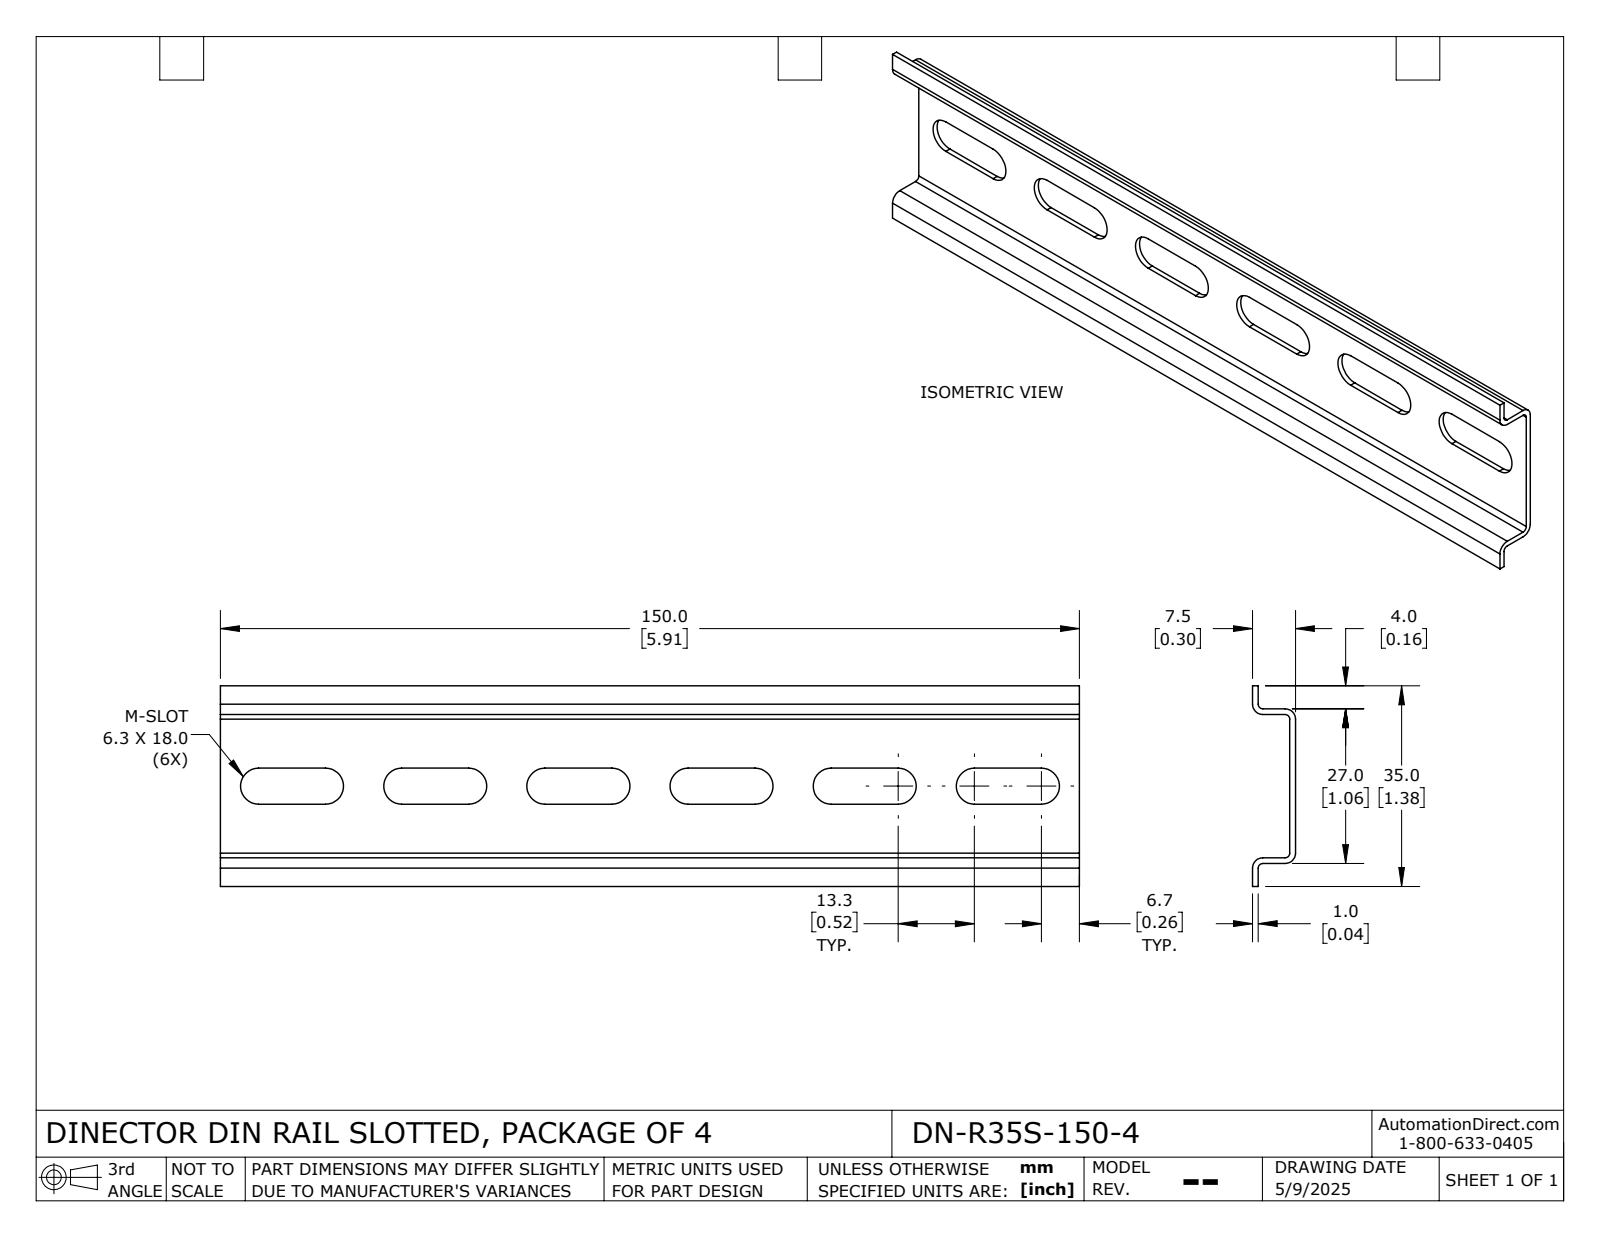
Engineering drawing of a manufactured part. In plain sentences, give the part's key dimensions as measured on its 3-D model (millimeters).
The part is named "DN-R35S-150-4_Default". Its 3-D file was written by "SolidWorks 2024 (CONFIG_CONTROL_DESIGN)". It is 1 solid with 46 faces: 26 planar, 20 cylindrical and 0 other. Overall it measures 150 by 35 by 7.5 millimeters. Its volume is 6 236 cubic millimeters and its surface area 13 123 square millimeters. Partial cylindrical surfaces (rounded edges, fillets, slot ends): 12 of radius 3.15, 4 of radius 0.8, 4 of radius 1.8. The main face-to-face distances are 1, 6.5, 26, 7.5, 5.5, 27, 25, 4, 5, 30.
